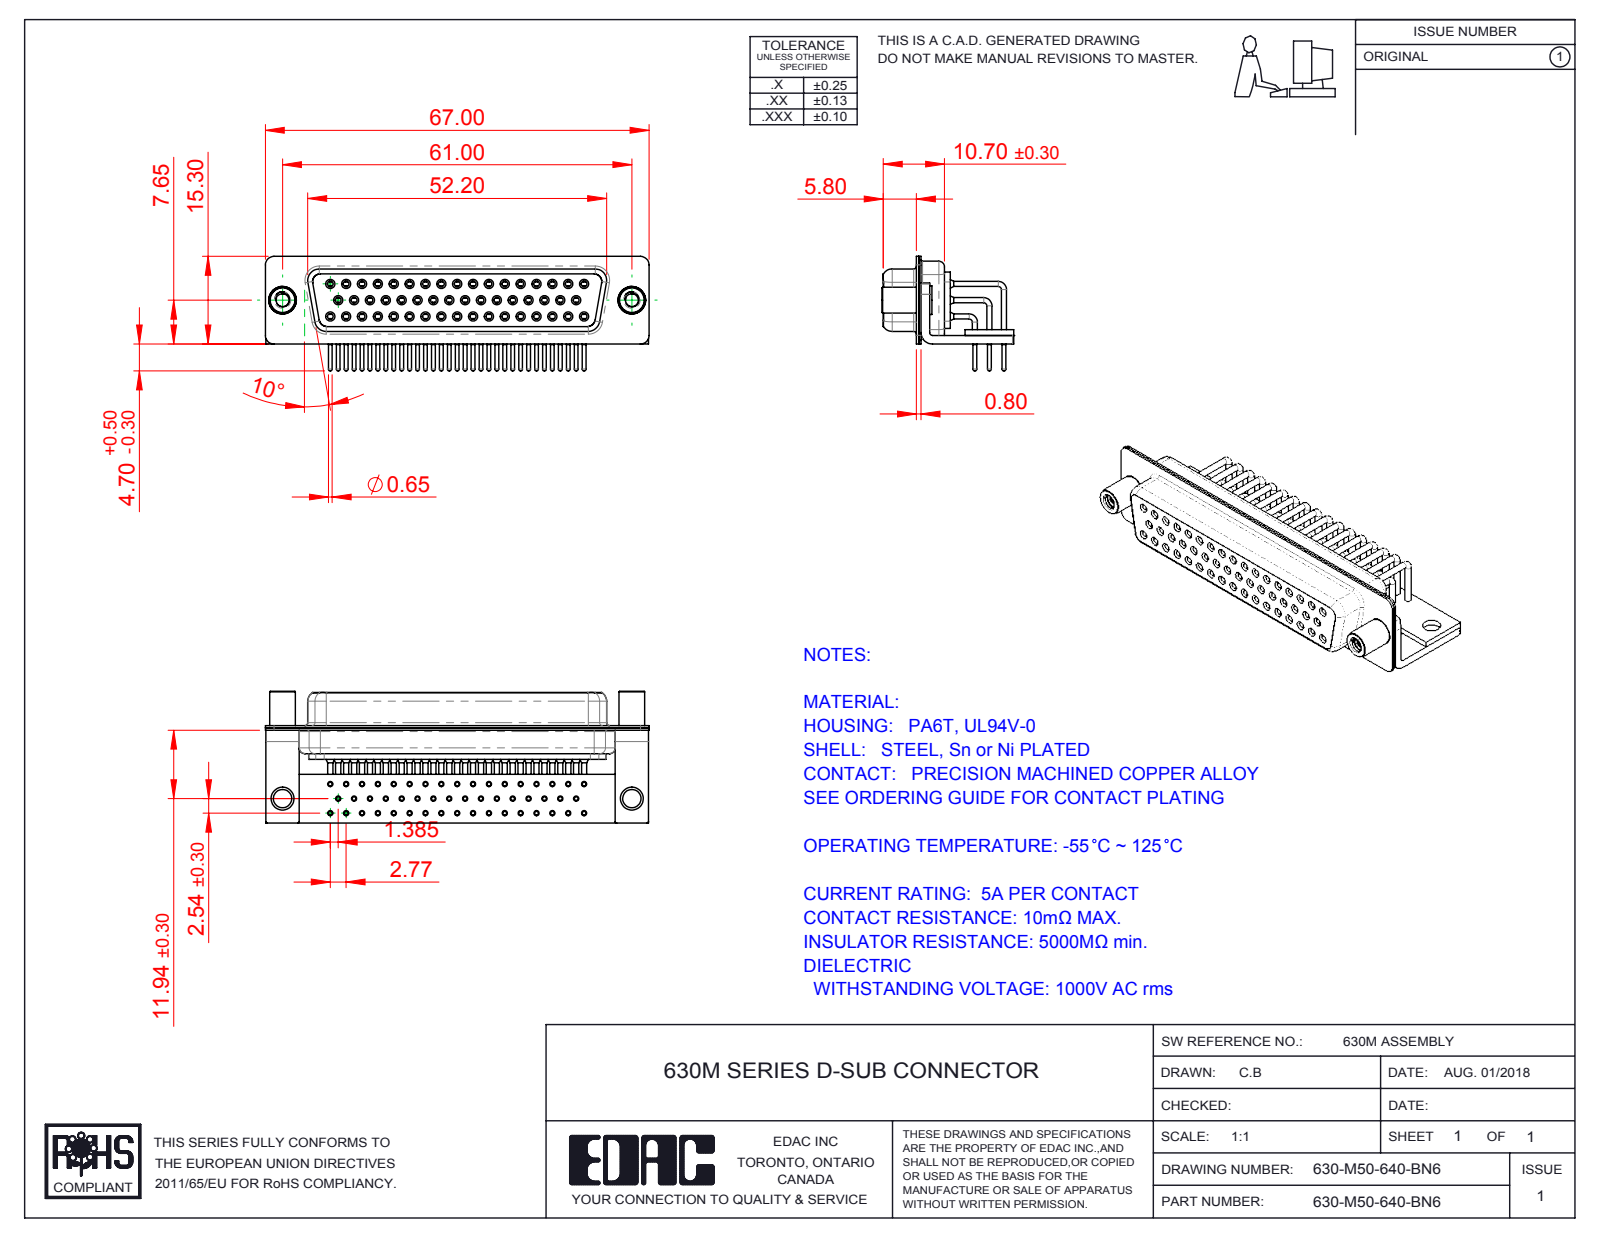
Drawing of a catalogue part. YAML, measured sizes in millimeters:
part_name: "630M Contact Row 3; 630M Contact Row 1_50 Contacts; 630M Stabilizer Bracket_50 Contacts; 630M 4-40 Threaded Standoff (+6 more)"
step_written_by: "SolidWorks 2016 (CONFIG_CONTROL_DESIGN)"
units: millimeters
bodies: {solids: 58, faces: 3129, planar: 845, cylindrical: 1451, other: 833}
overall_size: [67, 23, 20]
volume: 7991
surface_area: 18922
round_holes:
  - {diameter: 0.9, count: 50}
  - {diameter: 1, count: 50}
  - {diameter: 1.1, count: 50}
  - {diameter: 1.7, count: 50}
  - {diameter: 1.8, count: 50}
  - {diameter: 2, count: 50}
  - {diameter: 2.26, count: 2}
  - {diameter: 3.2, count: 2}
  - {diameter: 4, count: 2}
  - {diameter: 4.8, count: 2}
round_bosses_or_shafts:
  - {diameter: 0.9, count: 59}
  - {diameter: 1.6, count: 50}
  - {diameter: 1.5, count: 50}
  - {diameter: 0.65, count: 50}
  - {diameter: 5, count: 2}
  - {diameter: 4.9, count: 2}
  - {diameter: 4.5, count: 2}
partial_cylinders:
  - {radius: 0.25, count: 16}
  - {radius: 1.5, count: 16}
  - {radius: 2, count: 13}
  - {radius: 1.35, count: 8}
  - {radius: 1.6, count: 8}
  - {radius: 0.5, count: 5}
  - {radius: 0.6, count: 4}
  - {radius: 0.65, count: 4}
face_to_face_distances: [0.4, 1, 2.2, 0.85, 1.35, 11.85, 12.25, 5.8, 0.8, 5.9]
hole_center_spacings: [2.77, 5.54, 8.31, 11.08, 13.85, 16.62, 3.16, 19.39]
